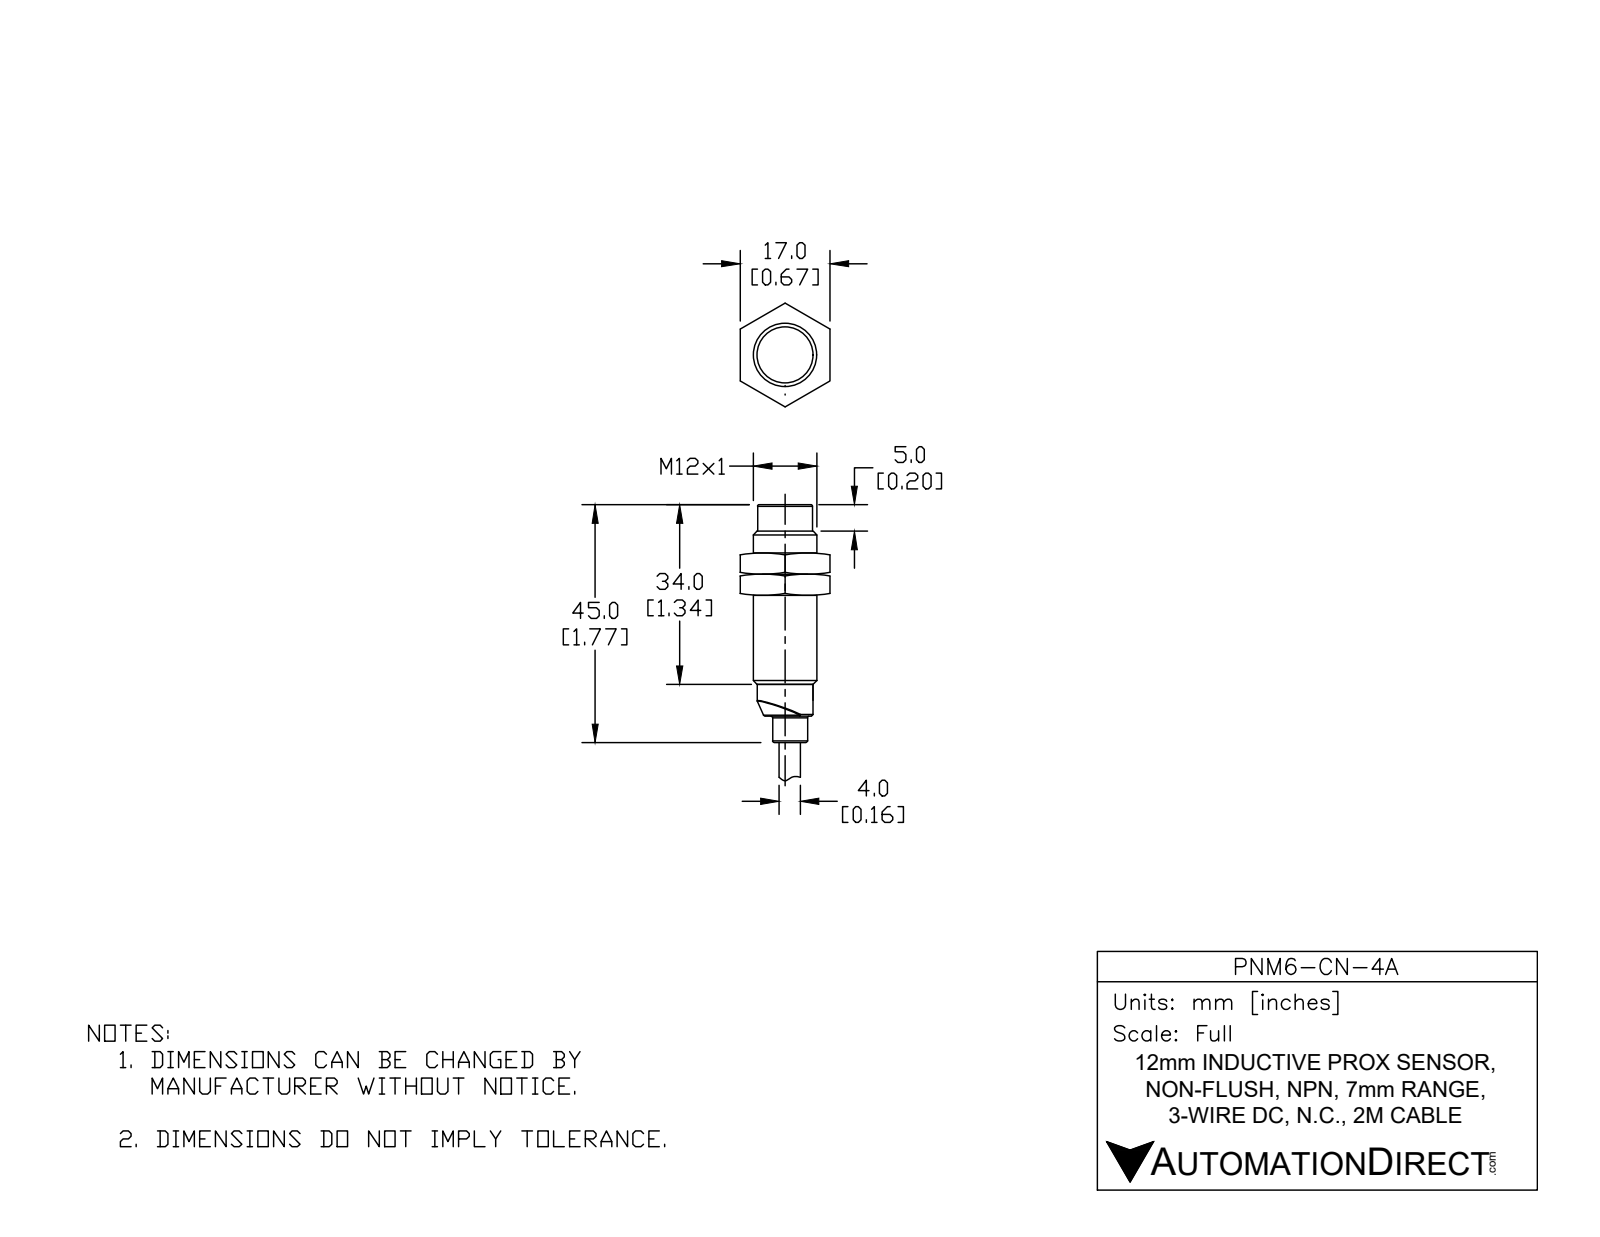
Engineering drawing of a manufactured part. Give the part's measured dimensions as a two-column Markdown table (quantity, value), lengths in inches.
| quantity | value |
| --- | --- |
| part name | PNM6-CN-4A |
| STEP written by | SolidWorks 2017 (AUTOMOTIVE_DESIGN) |
| units | inches |
| bodies | 1 solid, 59 faces (13 planar, 23 cylindrical, 23 other) |
| overall size | 3.772 × 0.472 × 0.472 |
| volume | 0.313 in³ |
| surface area | 4.04 in² |
| round holes (diameter × count) | 0.161 × 1 |
| round bosses / shafts (diameter × count) | 0.049 × 3, 0.472 × 1, 0.417 × 1, 0.415 × 1, 0.26 × 1, 0.157 × 1 |
| partial cylindrical surfaces (radius × count) | 0.025 × 1, 0.077 × 1 |
| main face-to-face distances | 1.575, 1.772, 0.197, 3.772, 2.197, 2, 1.457, 0.118, 0.315, 2.315 |
